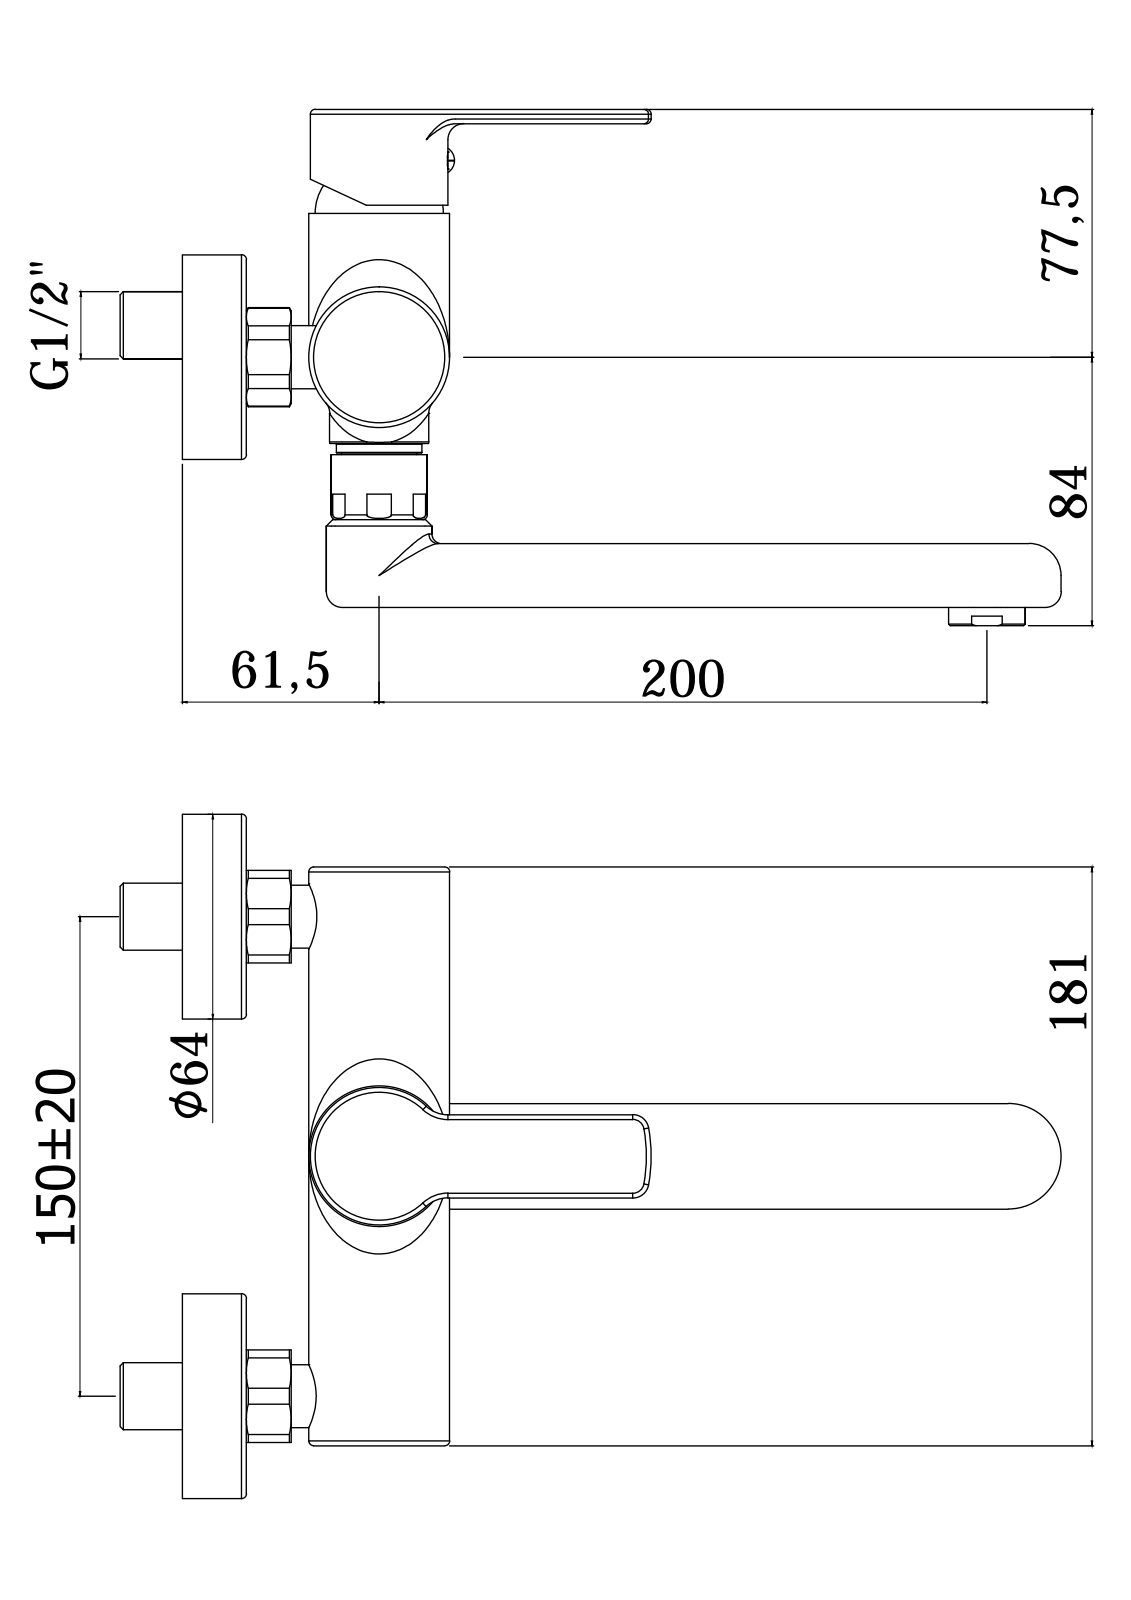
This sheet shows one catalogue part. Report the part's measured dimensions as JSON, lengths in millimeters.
{"part_name": "RED161CR", "step_written_by": "CREO PARAMETRIC BY PTC INC, 2020044 (CONFIG_CONTROL_DESIGN)", "units": "millimeters", "bodies": {"solids": 3, "faces": 3002, "planar": 2185, "cylindrical": 462, "other": 355}, "overall_size": [271.5, 213.5, 153.93], "volume_mm3": 224061, "surface_area_mm2": 176236, "round_holes": [[9, 3], [12, 3], [3.3, 2], [4, 2], [7, 2], [8, 2], [10.5, 2], [18, 2], [20.5, 2], [21.5, 2], [24.1, 2], [25, 2]], "round_bosses_or_shafts": [[24, 3], [63.5, 2], [44, 2], [28, 2], [27, 2], [19.7, 2], [9, 2], [43, 1]], "partial_cylinders_radius": [[0.5, 83], [0.15, 11], [0.3, 9], [7, 6], [1, 4], [1.5, 4], [10, 3], [5, 2]], "face_to_face_distances": [1, 15, 0.6, 16, 14, 3, 140, 139, 125, 124], "hole_center_spacings": [0.71, 8.51, 8.6, 13.04, 13.21, 13.51, 89.86, 97.31]}
